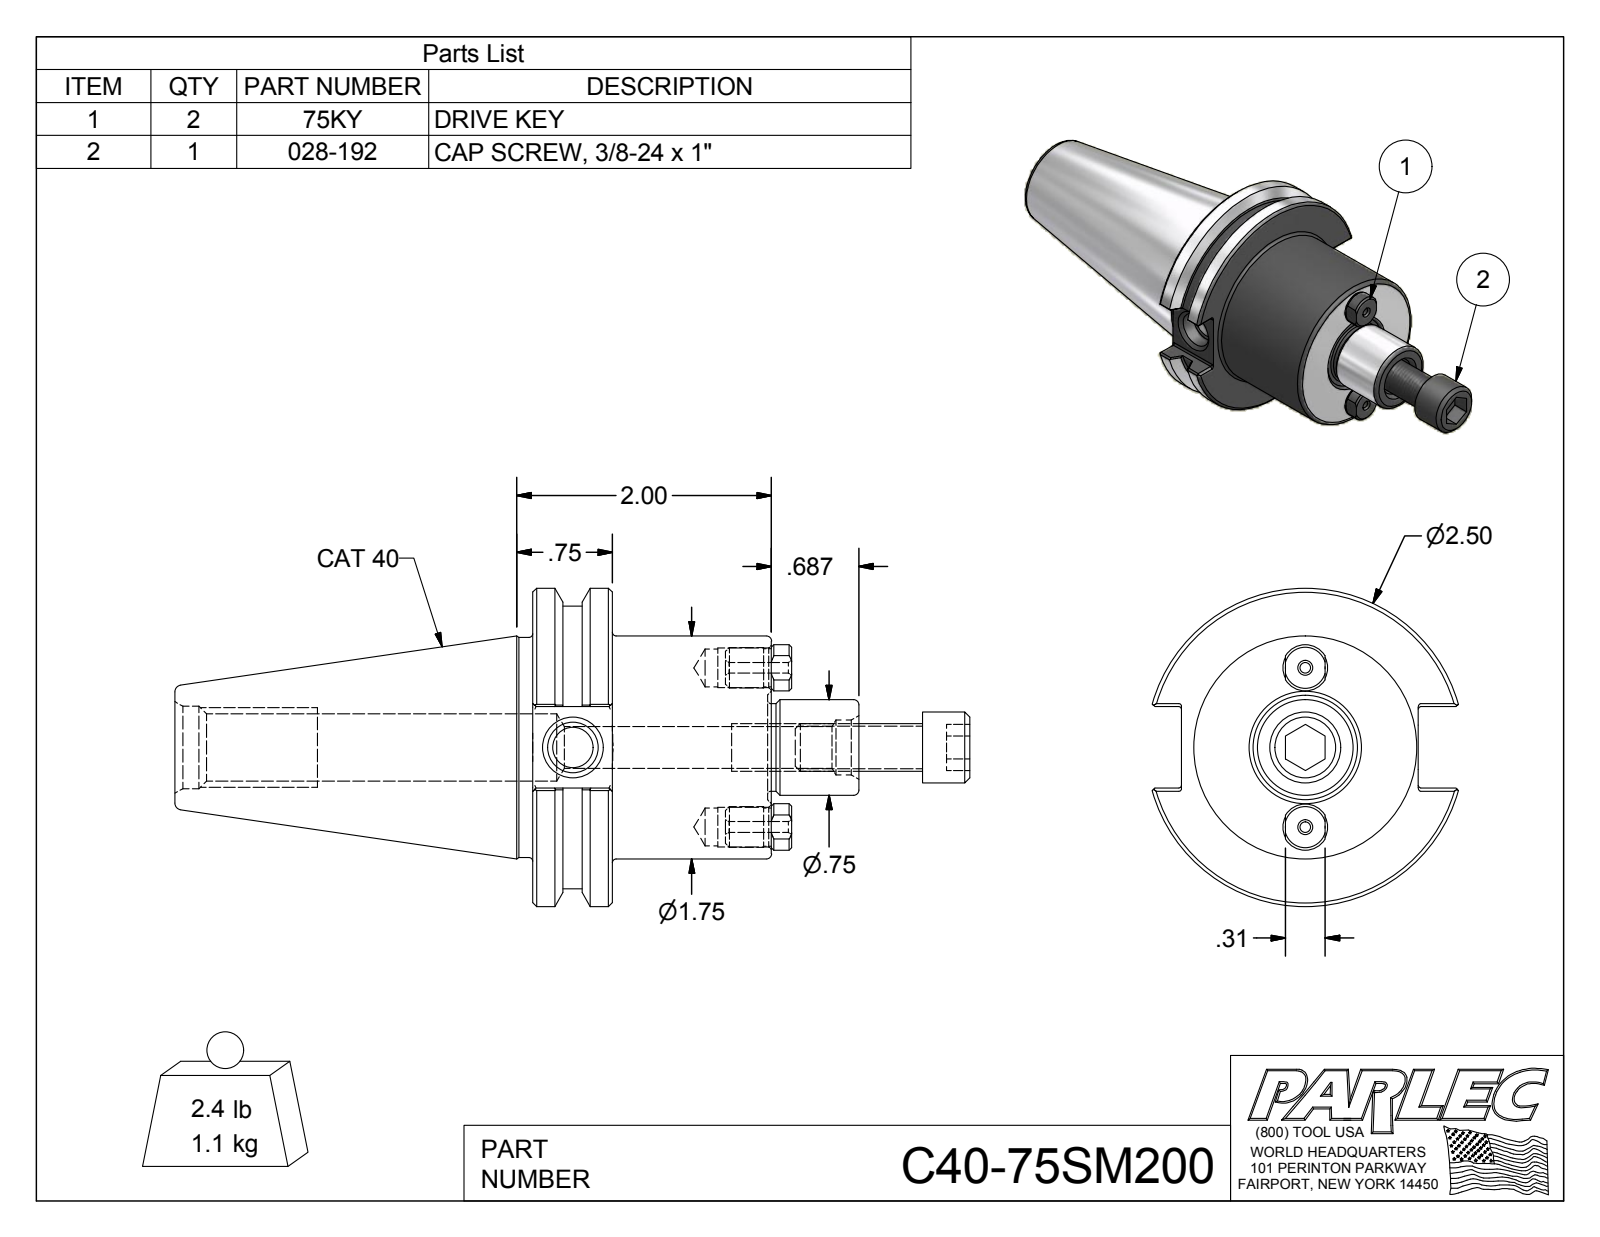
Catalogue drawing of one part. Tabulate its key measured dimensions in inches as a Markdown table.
| quantity | value |
| --- | --- |
| part name | C40-75SM200; C40-75SM200-1; 75KY; 028-192 |
| STEP written by | Autodesk Inventor 2012 (AUTOMOTIVE_DESIGN) |
| units | inches |
| bodies | 4 solids, 154 faces (57 planar, 44 cylindrical, 53 other) |
| overall size | 6.246 × 2.5 × 2.406 |
| volume | 9.478 in³ |
| surface area | 46.81 in² |
| round holes (diameter × count) | 0.084 × 2, 0.297 × 2, 0.312 × 2, 0.315 × 1, 0.33 × 1, 0.399 × 1, 0.43 × 1, 0.527 × 1, 0.648 × 1 |
| round bosses / shafts (diameter × count) | 0.318 × 2, 0.3 × 2, 2.5 × 1, 2.219 × 1, 1.75 × 1, 1.73 × 1, 0.75 × 1, 0.69 × 1 |
| partial cylindrical surfaces (radius × count) | 0.02 × 12, 0.183 × 2 |
| main face-to-face distances | 0.625, 1.875, 1.25, 0.64, 0.5, 1.86, 2.812, 3.437, 4.687, 3.201 |
| hole center spacings | 0.625, 1.25 |
